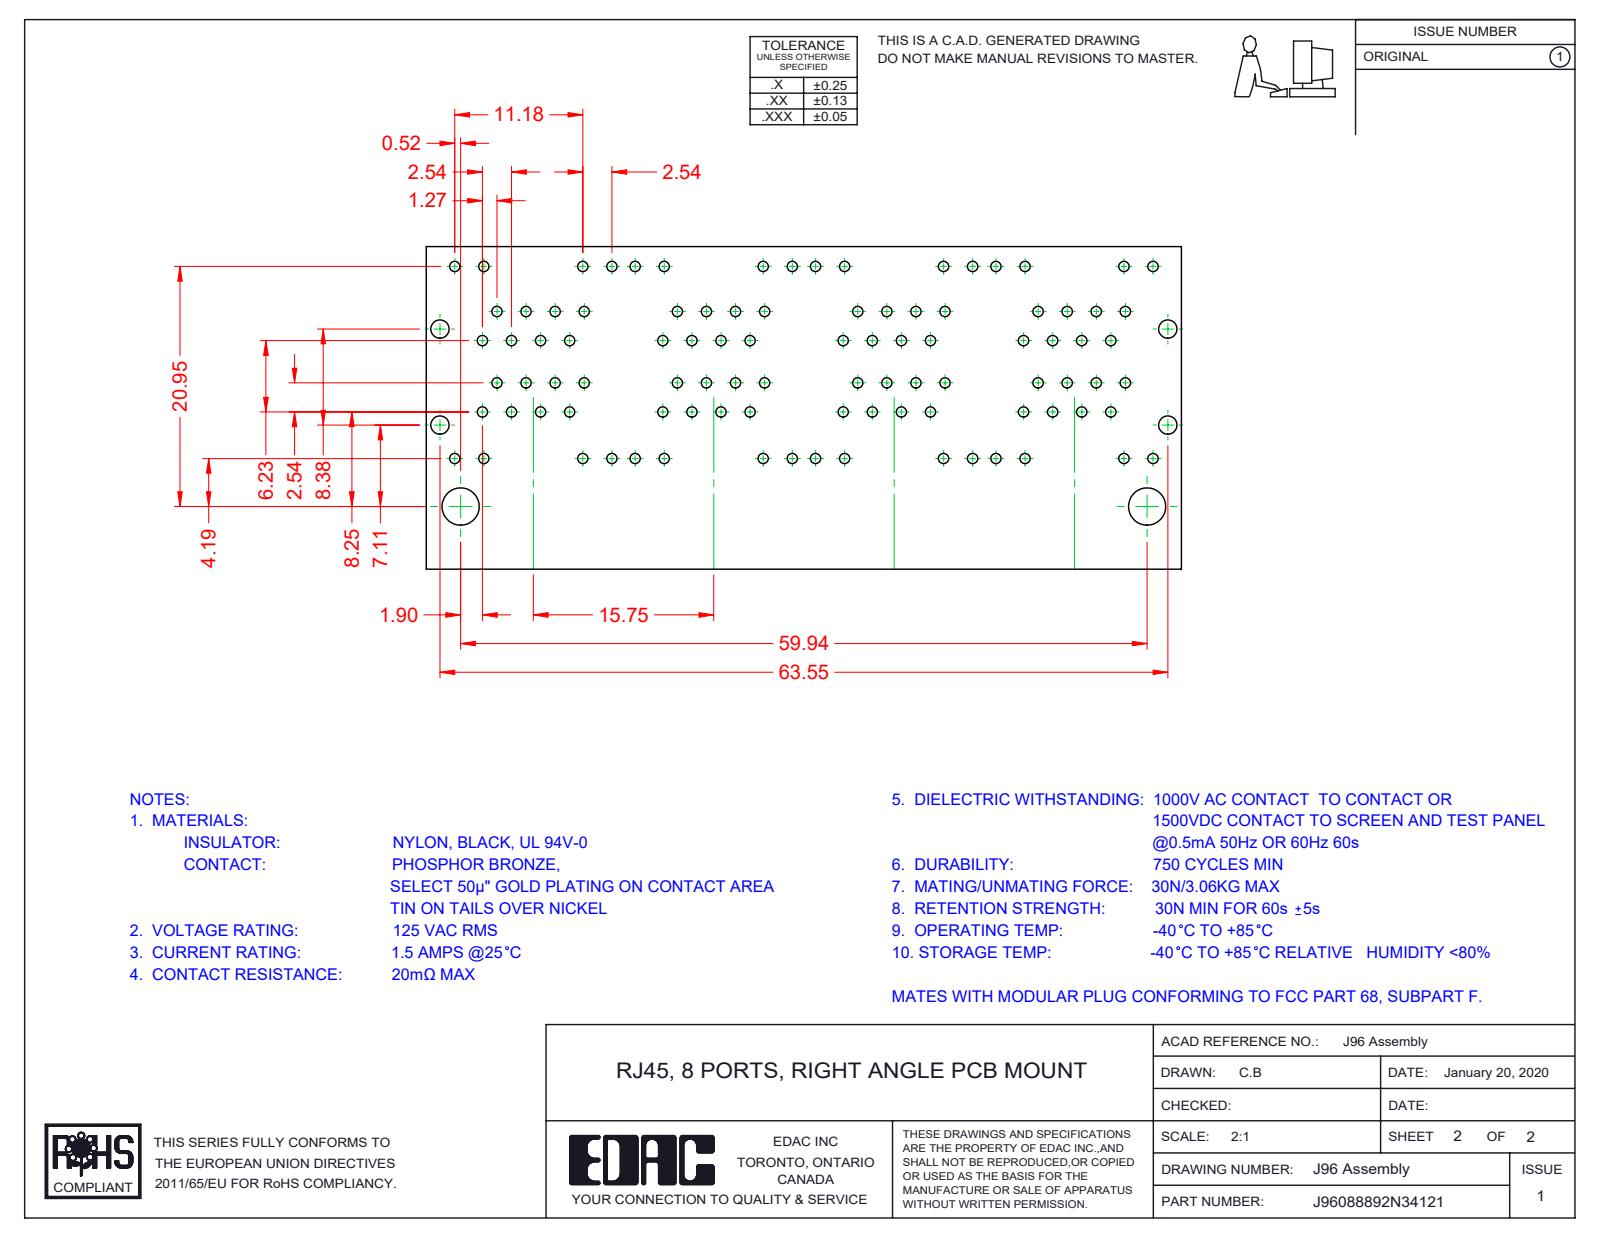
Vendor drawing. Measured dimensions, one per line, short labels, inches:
name: 96 Contacts Upper; 96 Grounding_8 Ports; 96 Back Plate_8 Ports; 96 Contacts Lower (+8 more)
written by: SolidWorks 2016 (CONFIG_CONTROL_DESIGN)
unit: in
bodies: 96 solids, 7642 faces (6069 planar, 1307 cylindrical, 266 other)
size: 2.522 × 1.165 × 1.129
volume: 1.474 in³; area: 98.67 in²
holes: 3× ⌀0.067
bosses: 3× ⌀0.066
rounds: 124× R0.01, 73× R0.014, 72× R0.039, 49× R0.02, 32× R0.036, 21× R0.008, 11× R0.028, 8× R0.009
face distances: 0.62, 0.014, 0.392, 0.046, 0.063, 0.021, 0.393, 0.401, 0.499, 0.133
hole spacings: 0.62, 1.24
